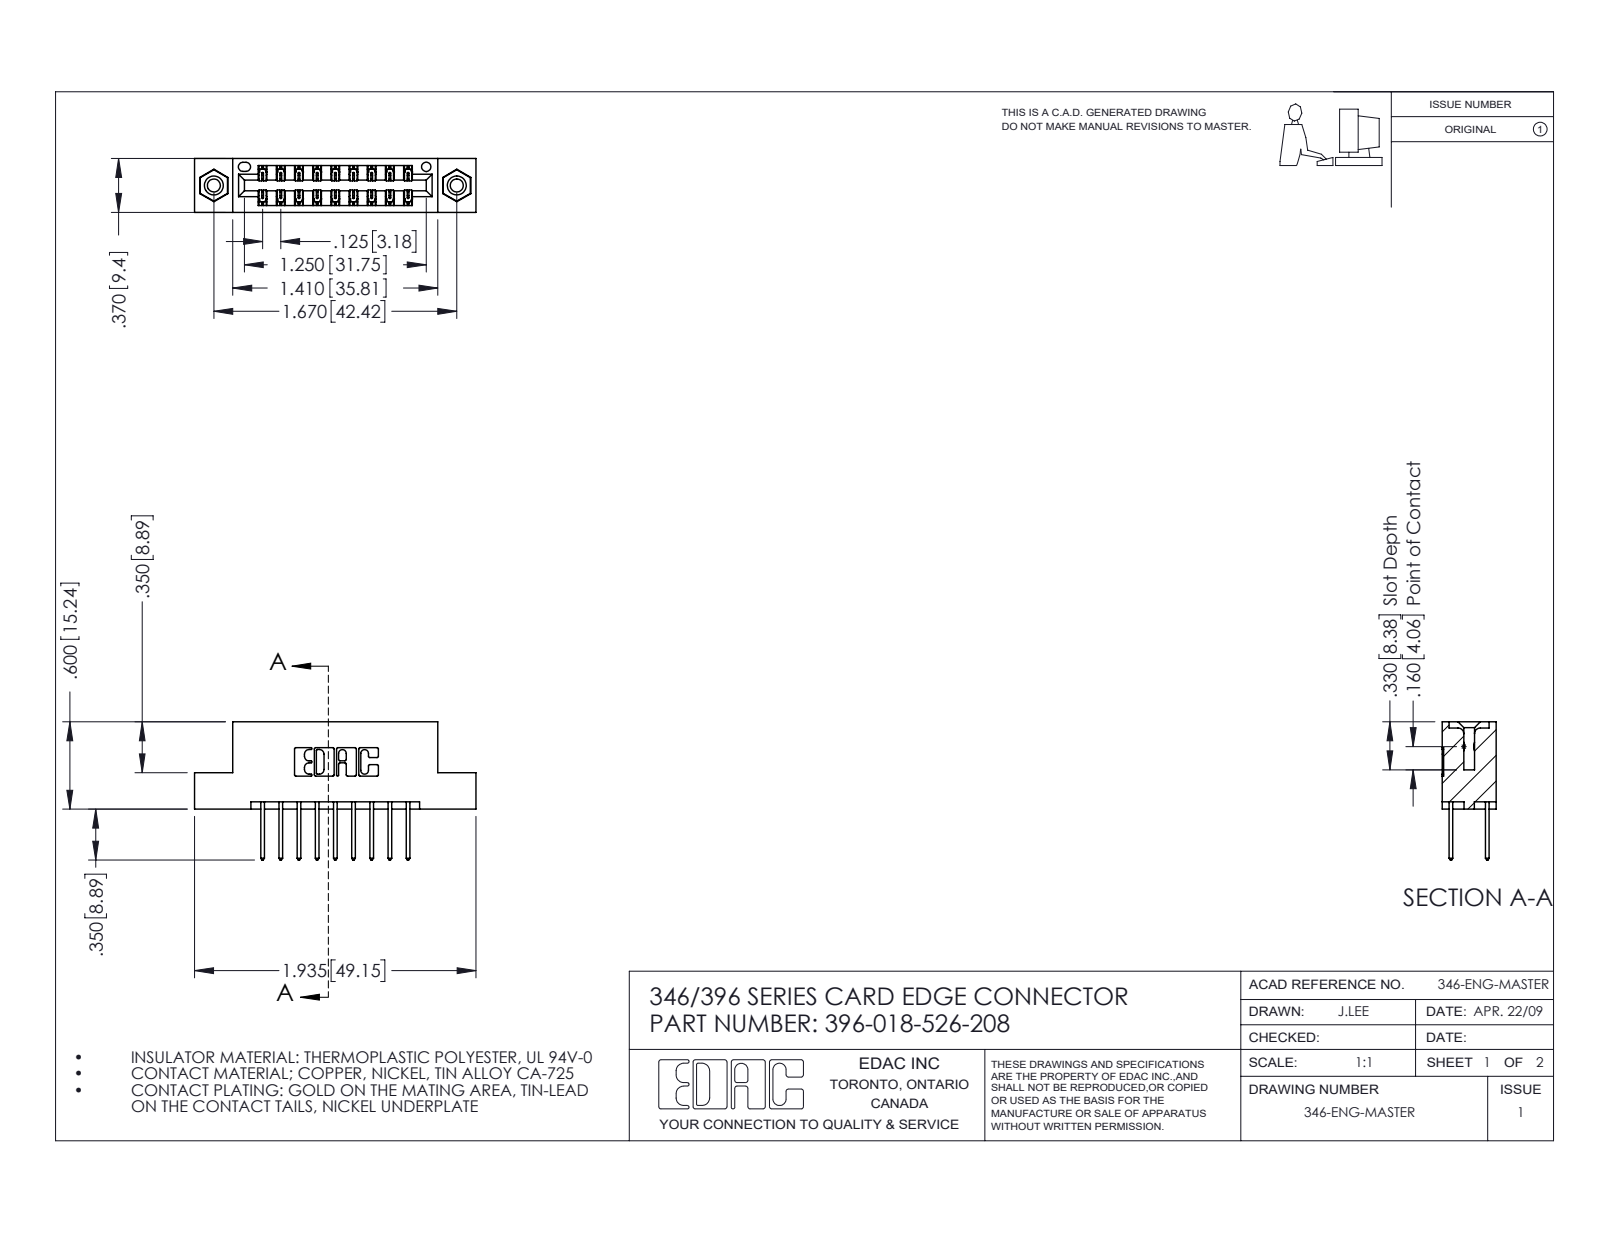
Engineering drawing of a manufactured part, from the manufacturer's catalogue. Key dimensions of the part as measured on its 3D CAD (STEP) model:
Part name (STEP PRODUCT): 345-250-001_345-250-003-102; 346 Part_Flush Mounting Lugs - 0.156 Dia-TI; 345-292-001_345-293-126; 396-018-526-208
STEP written by: SolidWorks 2016 (CONFIG_CONTROL_DESIGN)
Units: inches
Bodies: 21 solids, 1118 faces (738 planar, 364 cylindrical, 16 other)
Overall size (bounding box): 1.935 × 0.95 × 0.37
Volume: 0.278 in³ · Surface area: 9.146 in²
Round holes (diameter × count): ⌀0.089 ×2, ⌀0.125 ×2, ⌀0.156 ×2, ⌀0.064 ×1
Round bosses / shafts (diameter × count): ⌀0.155 ×2
Partial cylindrical surfaces — rounded edges, fillets, slot ends (radius × count): R0.006 ×27, R0.01 ×22, R0.01 ×18, R0.007 ×6, R0.031 ×6, R0.026 ×3, R0.014 ×2, R0.022 ×2
Main face-to-face distances: 0.25, 0.048, 0.322, 0.37, 0.072, 0.298, 0.025, 0.275, 0.148, 0.222
Hole centre spacings: 0.246, 1.465, 1.67
